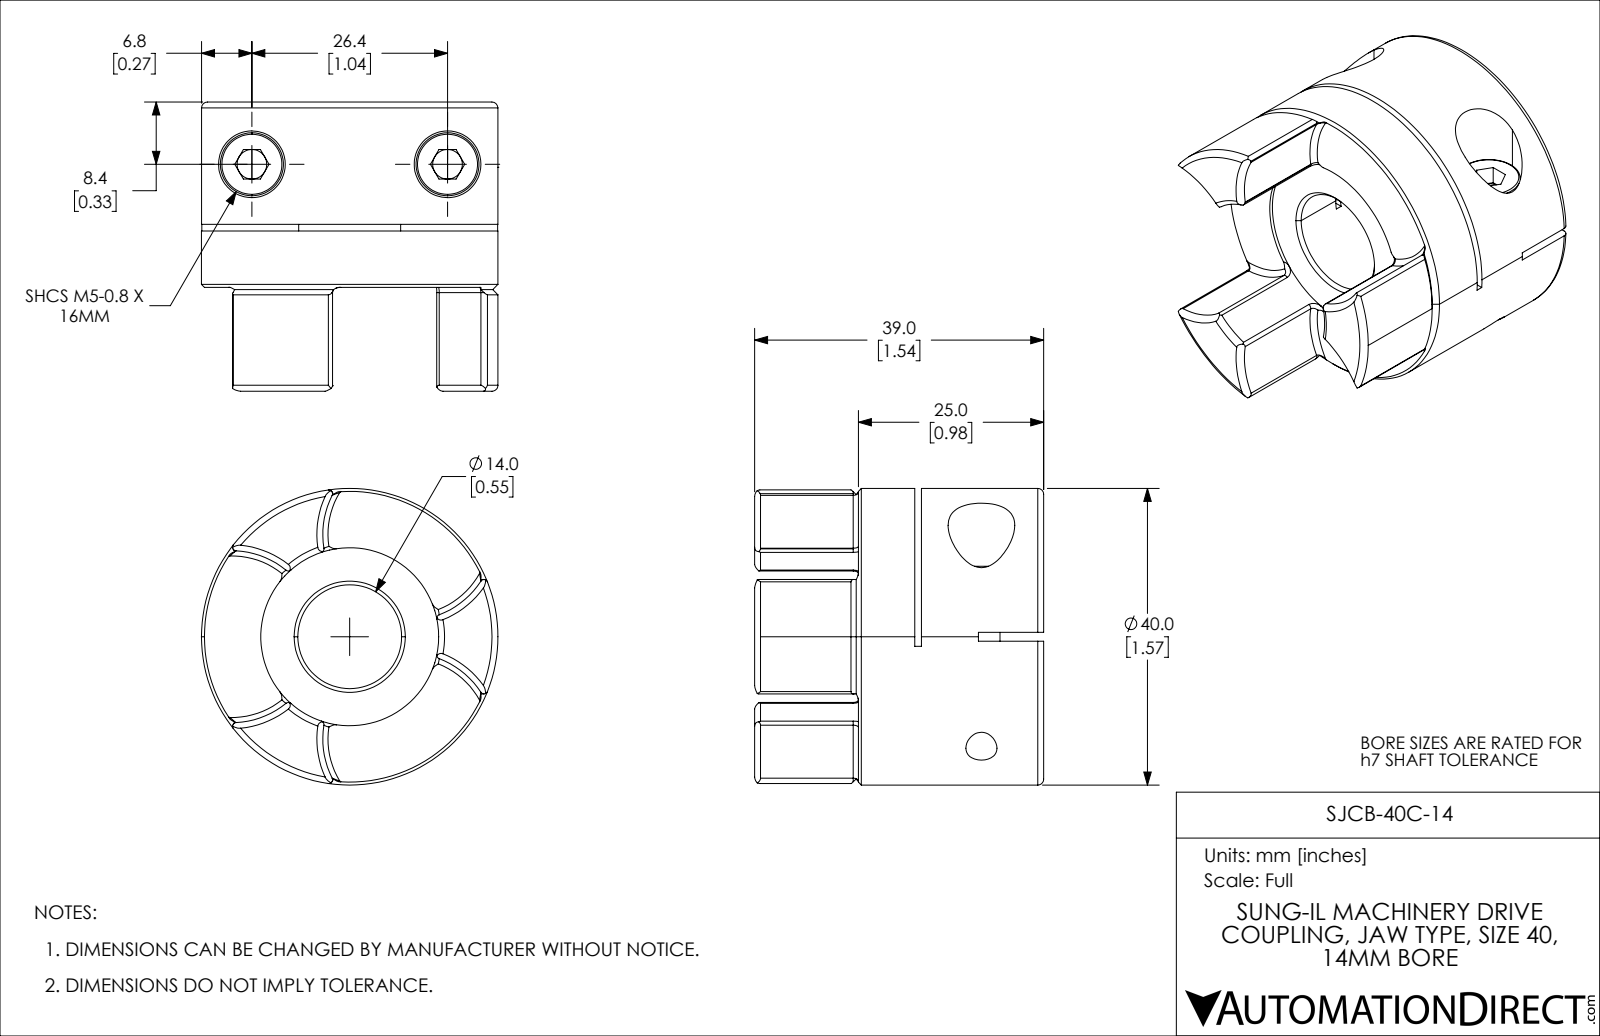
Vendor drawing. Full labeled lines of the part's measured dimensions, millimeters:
Part name (STEP PRODUCT): SJCB-40C-14
STEP written by: SolidWorks 2021 (CONFIG_CONTROL_DESIGN)
Units: millimetres
Bodies: 3 solids, 184 faces (50 planar, 68 cylindrical, 66 other)
Overall size (bounding box): 40 × 40 × 39
Volume: 29 005 mm³ · Surface area: 11 643 mm²
Round holes (diameter × count): ⌀4 ×2, ⌀4.2 ×2, ⌀5.4 ×2, ⌀9 ×2, ⌀14 ×1, ⌀24 ×1
Round bosses / shafts (diameter × count): ⌀8.5 ×2, ⌀5 ×2, ⌀40 ×1
Partial cylindrical surfaces — rounded edges, fillets, slot ends (radius × count): R0.5 ×12, R11.6 ×3, R40 ×1
Main face-to-face distances: 17.4, 0.9, 16.5, 7.6, 8.5, 25, 1.2, 0.5, 7.1, 8
Hole centre spacings: 26.4
